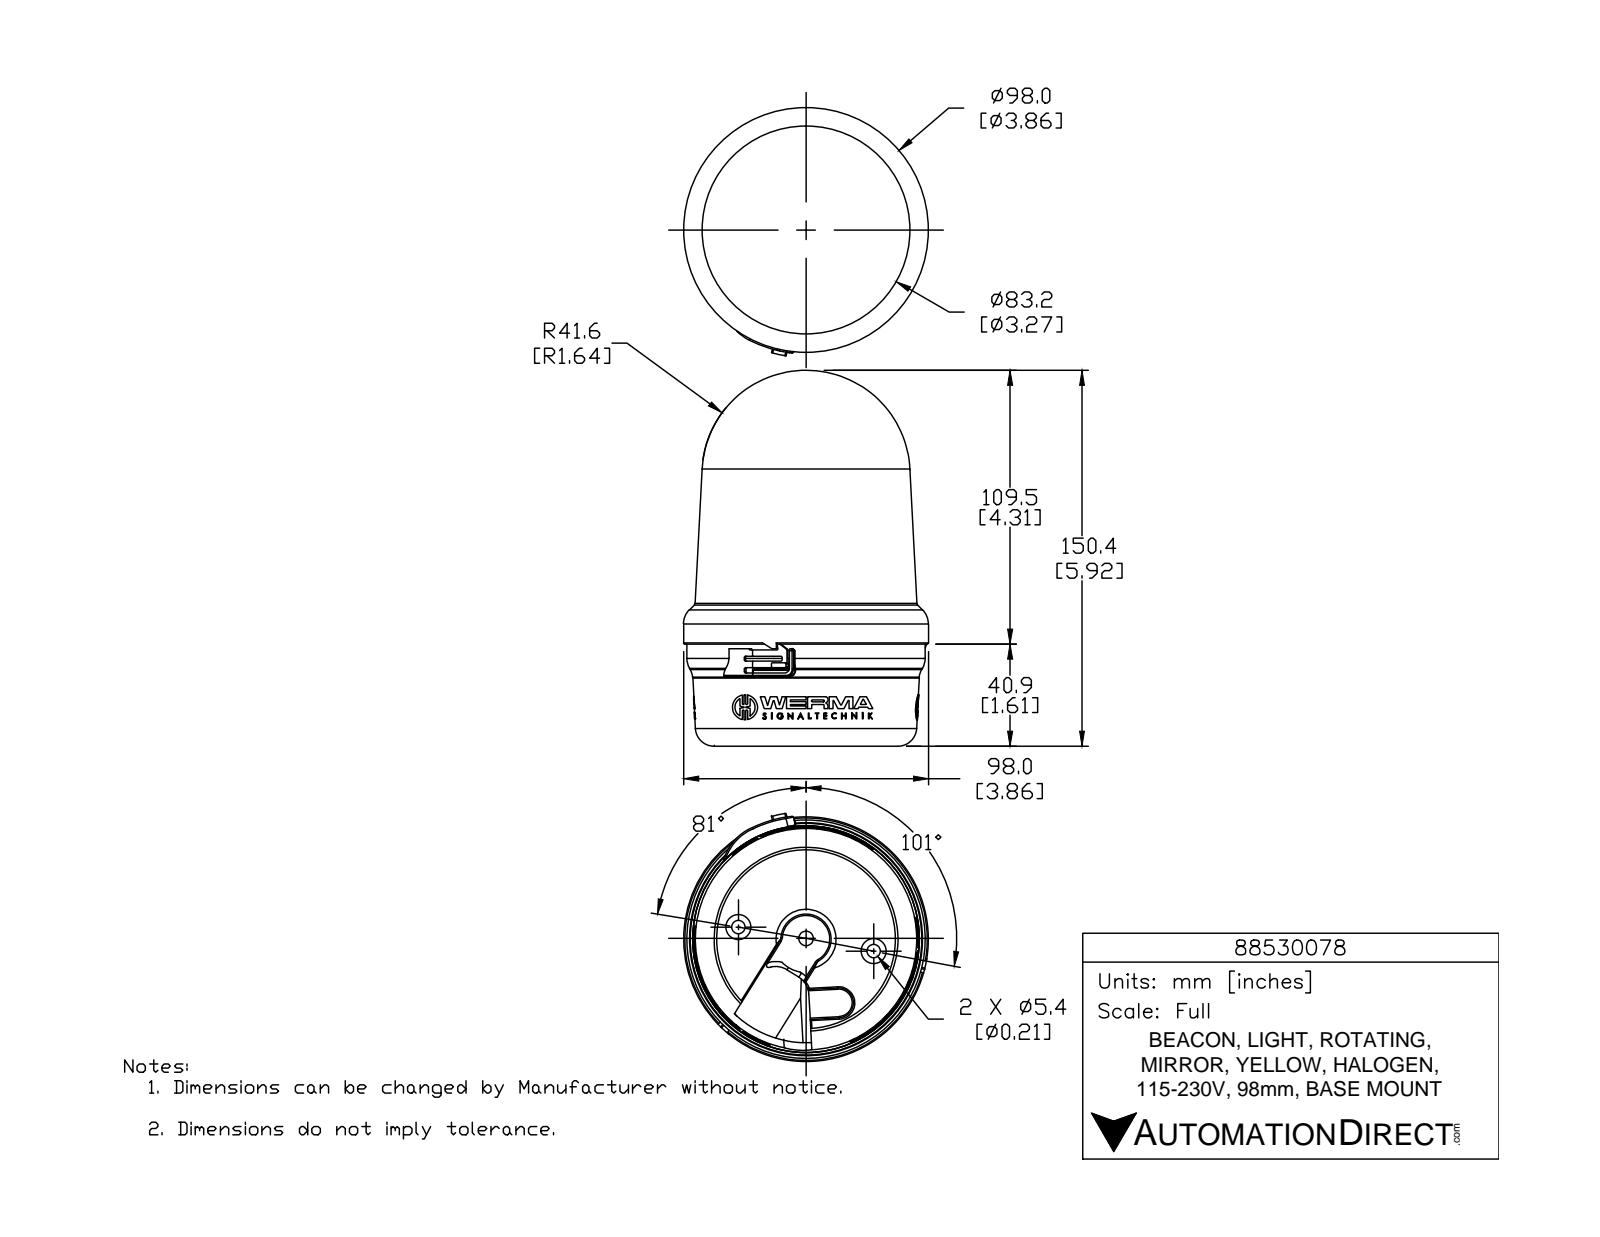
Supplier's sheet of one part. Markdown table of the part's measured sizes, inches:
| quantity | value |
| --- | --- |
| part name | 88530078 |
| STEP written by | SolidWorks 2015 (AUTOMOTIVE_DESIGN) |
| units | inches |
| bodies | 1 solid, 969 faces (586 planar, 238 cylindrical, 145 other) |
| overall size | 5.921 × 3.912 × 3.858 |
| volume | 49.51 in³ |
| surface area | 82.1 in² |
| round holes (diameter × count) | 0.068 × 3, 0.213 × 2, 0.409 × 2, 2.815 × 1 |
| round bosses / shafts (diameter × count) | 0.395 × 3, 0.099 × 3, 0.394 × 2, 3.858 × 1, 3.756 × 1, 3.571 × 1 |
| partial cylindrical surfaces (radius × count) | 0.02 × 21, 0.006 × 9, 0.006 × 6, 0.014 × 6, 0.014 × 6, 0.014 × 6, 0.229 × 6, 0.079 × 4 |
| main face-to-face distances | 0.059, 0.033, 0.27, 0.02, 0.289, 0.734, 0.768, 0.315, 1.319, 1.26 |
| hole center spacings | 1.083, 2.165 |
